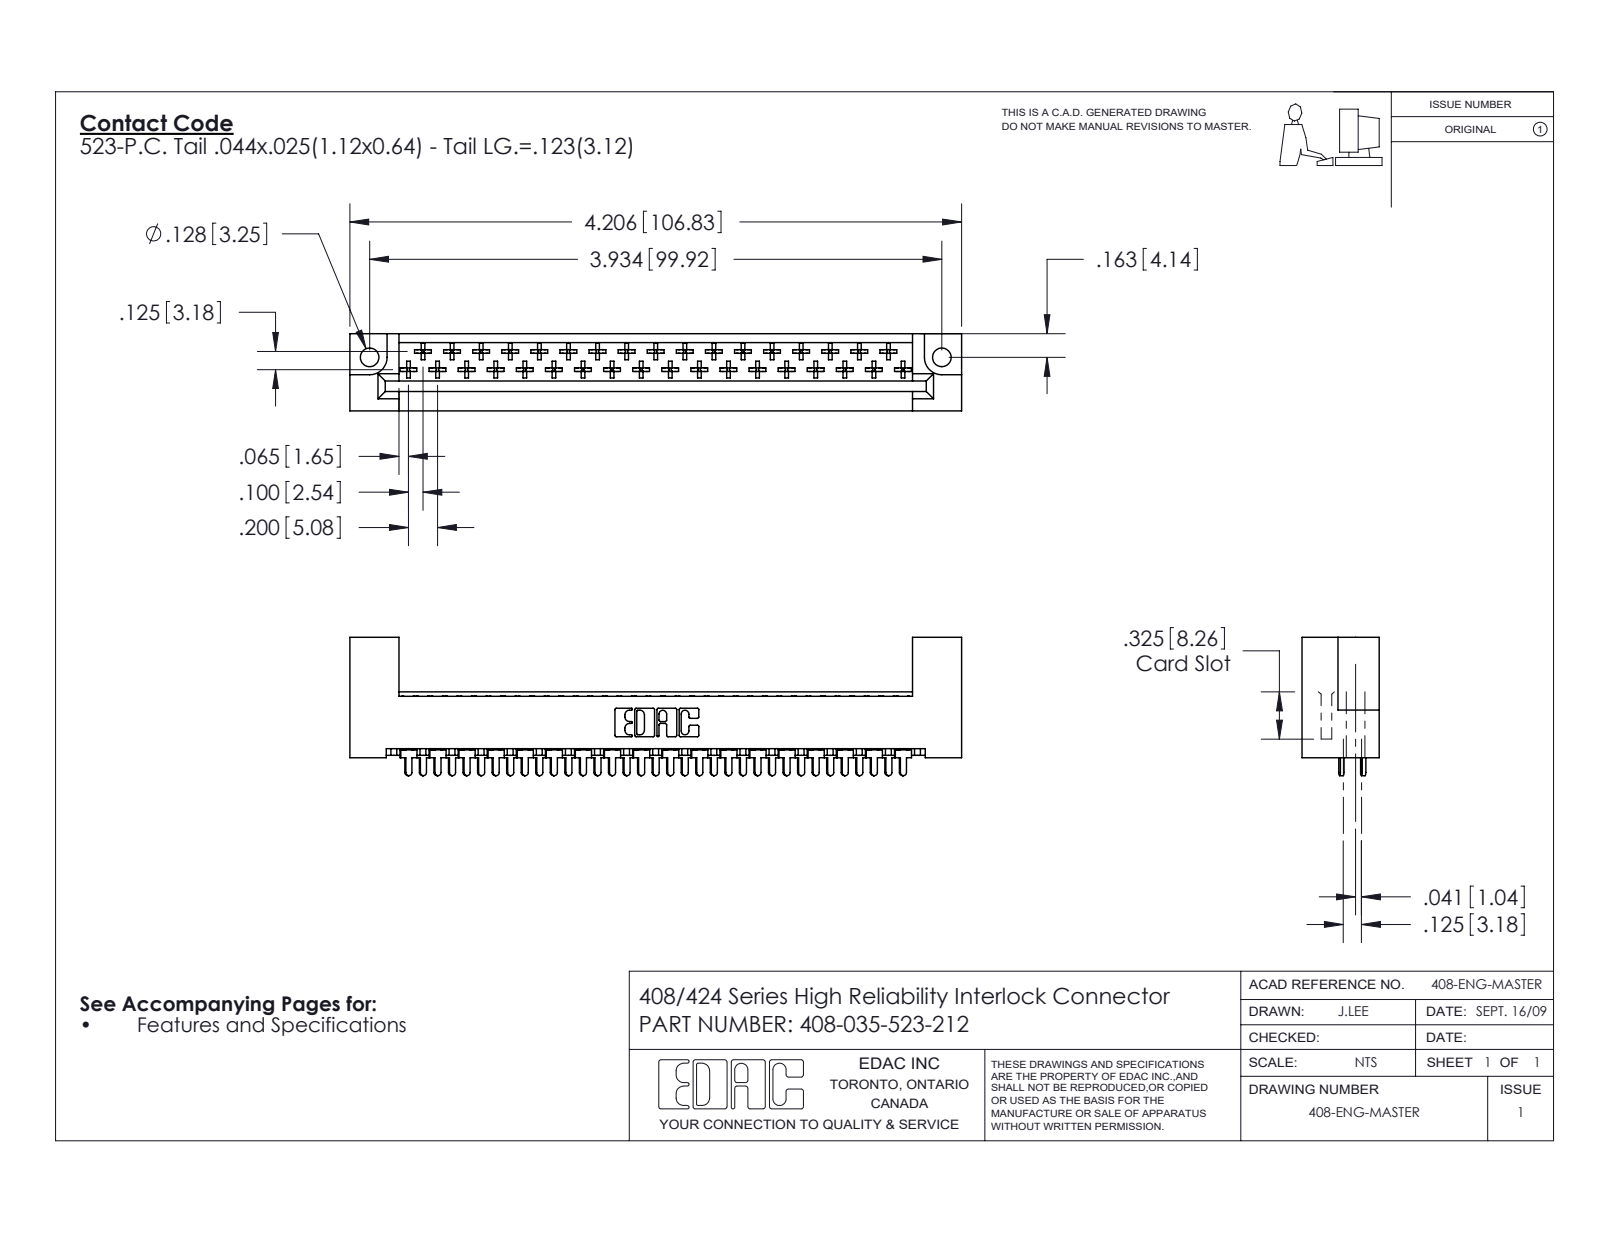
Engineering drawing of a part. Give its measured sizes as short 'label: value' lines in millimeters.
name: 408-035-523-212; 408-290-001_408-290-123 - Top; 408-290-001_408-290-123 - Bottom; 408 Part_035 - 2
written by: SolidWorks 2016 (CONFIG_CONTROL_DESIGN)
unit: mm
bodies: 36 solids, 2064 faces (1559 planar, 365 cylindrical, 140 other)
size: 106.8 × 24.2 × 13.5
volume: 13 300 mm³; area: 15 330 mm²
holes: 2× ⌀3.3
rounds: 210× R0.3, 37× R0.5, 35× R0.6, 22× R0.3, 6× R0.2, 6× R0.8, 3× R0.7, 2× R3
face distances: 13.5, 3.2, 2.5, 0.6, 0.6, 9.2, 6, 6.6, 10.1, 5.5
hole spacings: 99.9
